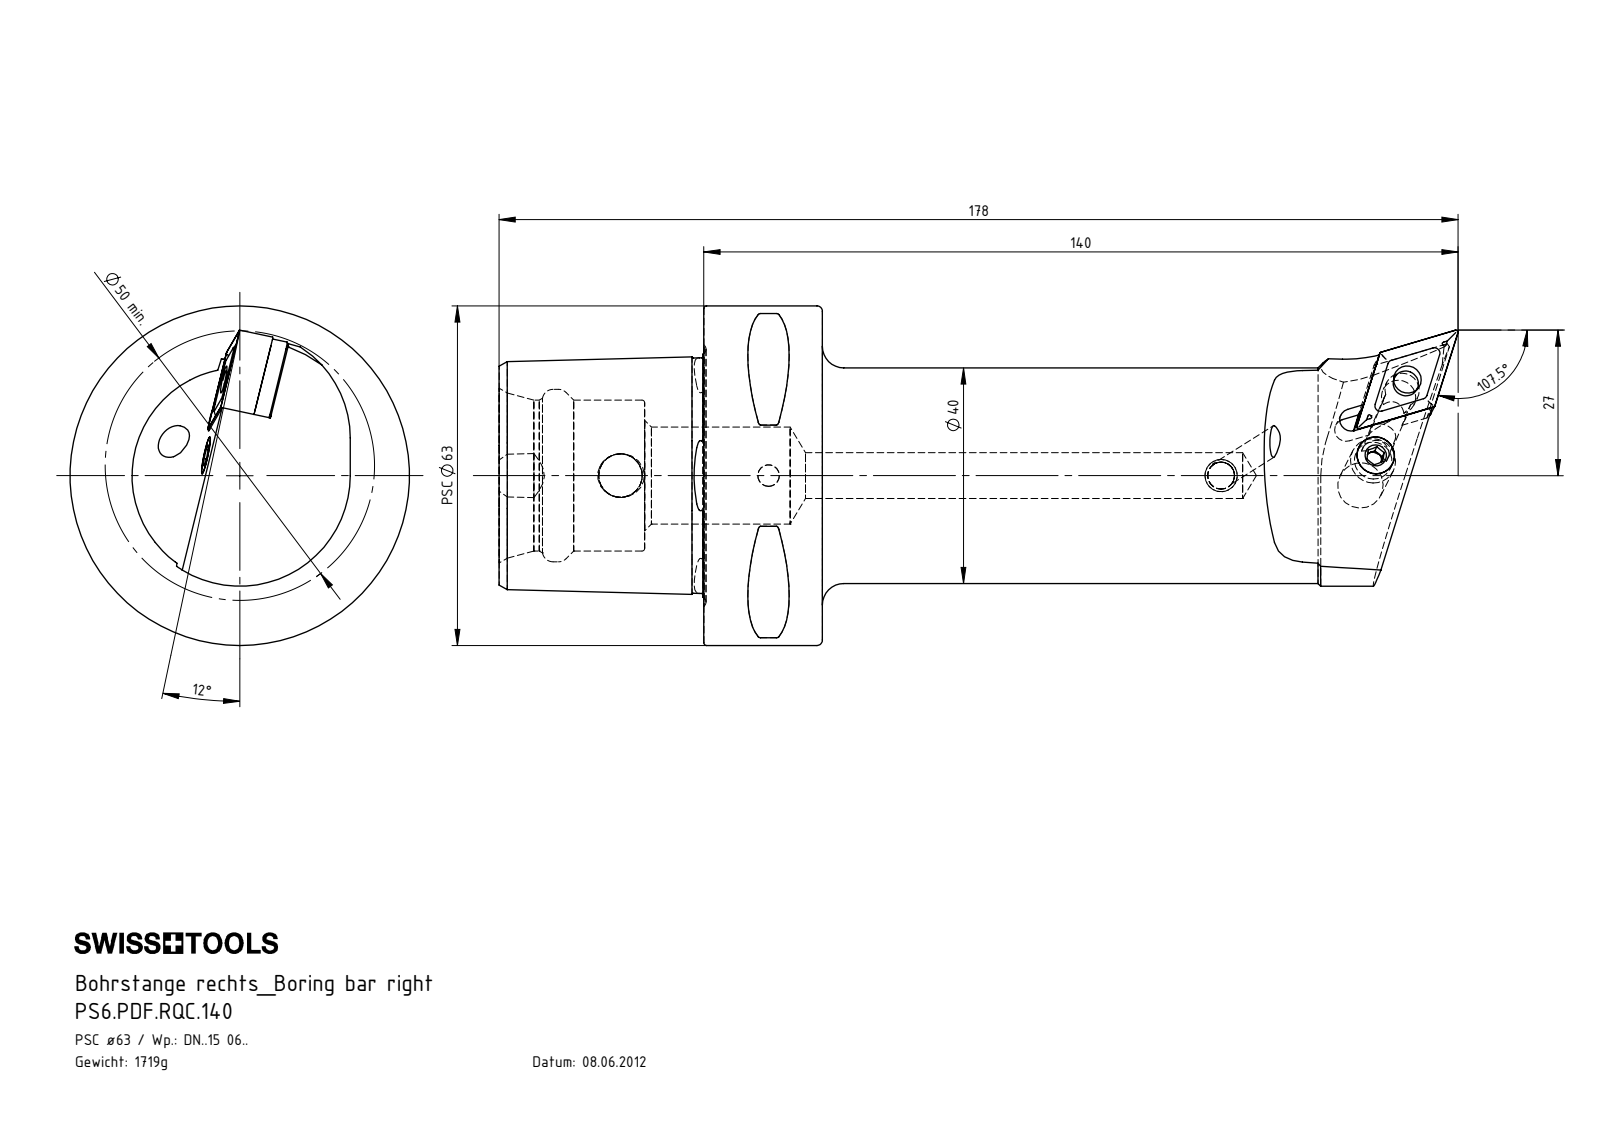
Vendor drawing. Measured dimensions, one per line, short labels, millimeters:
name: WDF-ER2.101.003_A; WCD-ER4.101.017_A; KVT_MB_600_060; PS6-PDF.RQC.140_A (+4 more)
written by: SolidWorks 2017 (AUTOMOTIVE_DESIGN)
unit: mm
bodies: 8 solids, 346 faces (92 planar, 87 cylindrical, 167 other)
size: 178 × 63 × 63
volume: 219 887 mm³; area: 39 988 mm²
holes: 1× ⌀4, 1× ⌀4.2, 1× ⌀5, 1× ⌀5.16, 1× ⌀6.4, 1× ⌀7, 1× ⌀8.1, 1× ⌀8.4, 1× ⌀8.5, 1× ⌀18, 1× ⌀28, 1× ⌀32
bosses: 1× ⌀63, 1× ⌀40, 1× ⌀8, 1× ⌀7.9, 1× ⌀6.4, 1× ⌀6, 1× ⌀4.7, 1× ⌀3.55
rounds: 8× R0.5, 4× R0.4, 4× R1, 2× R2.5, 1× R2.1, 1× R2.35, 1× R2.8, 1× R3
face distances: 22, 38, 60, 6.05, 12.27, 24.88, 3.18, 9.23, 27, 11
hole spacings: 15.61, 27.5, 84, 111.5
